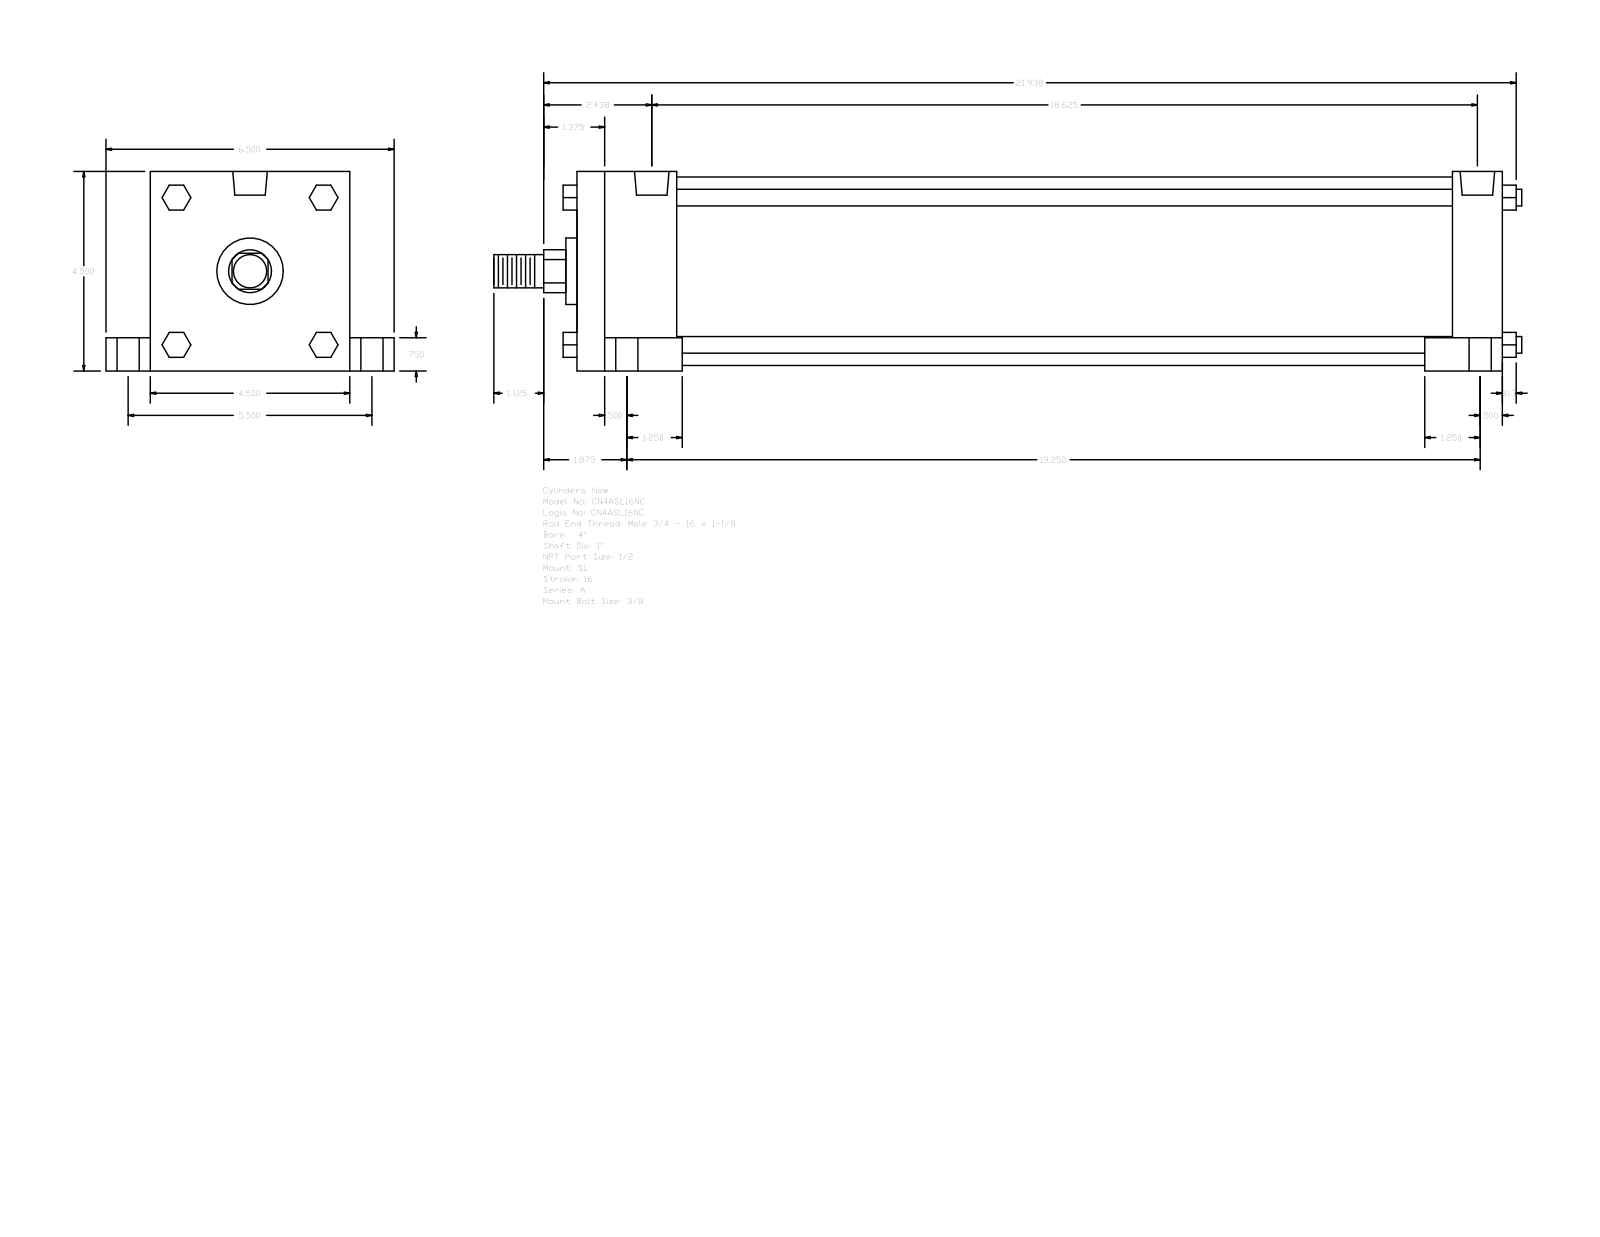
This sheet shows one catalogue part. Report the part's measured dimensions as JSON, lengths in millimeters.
{"part_name": "A_SL__0400_1", "step_written_by": "GSSL Pune (CONFIG_CONTROL_DESIGN)", "units": "millimeters", "bodies": {"solids": 0, "faces": 150, "planar": 114, "cylindrical": 36, "other": 0}, "overall_size": [588.96, 165.1, 114.3], "round_holes": [[8.73, 4], [12.7, 4], [19.05, 4], [19.77, 2]], "round_bosses_or_shafts": [[9.53, 4], [107.95, 1], [38.1, 1], [25.4, 1], [19.05, 1]], "partial_cylinders_radius": [[12.29, 1]], "face_to_face_distances": [114.3, 530.22, 28.57, 57.15, 473.07, 501.65, 444.5, 19.05, 25.4, 139.7], "hole_center_spacings": [3.18, 69.87, 70.01, 71.3, 72, 139.7, 466.72, 469.9]}
